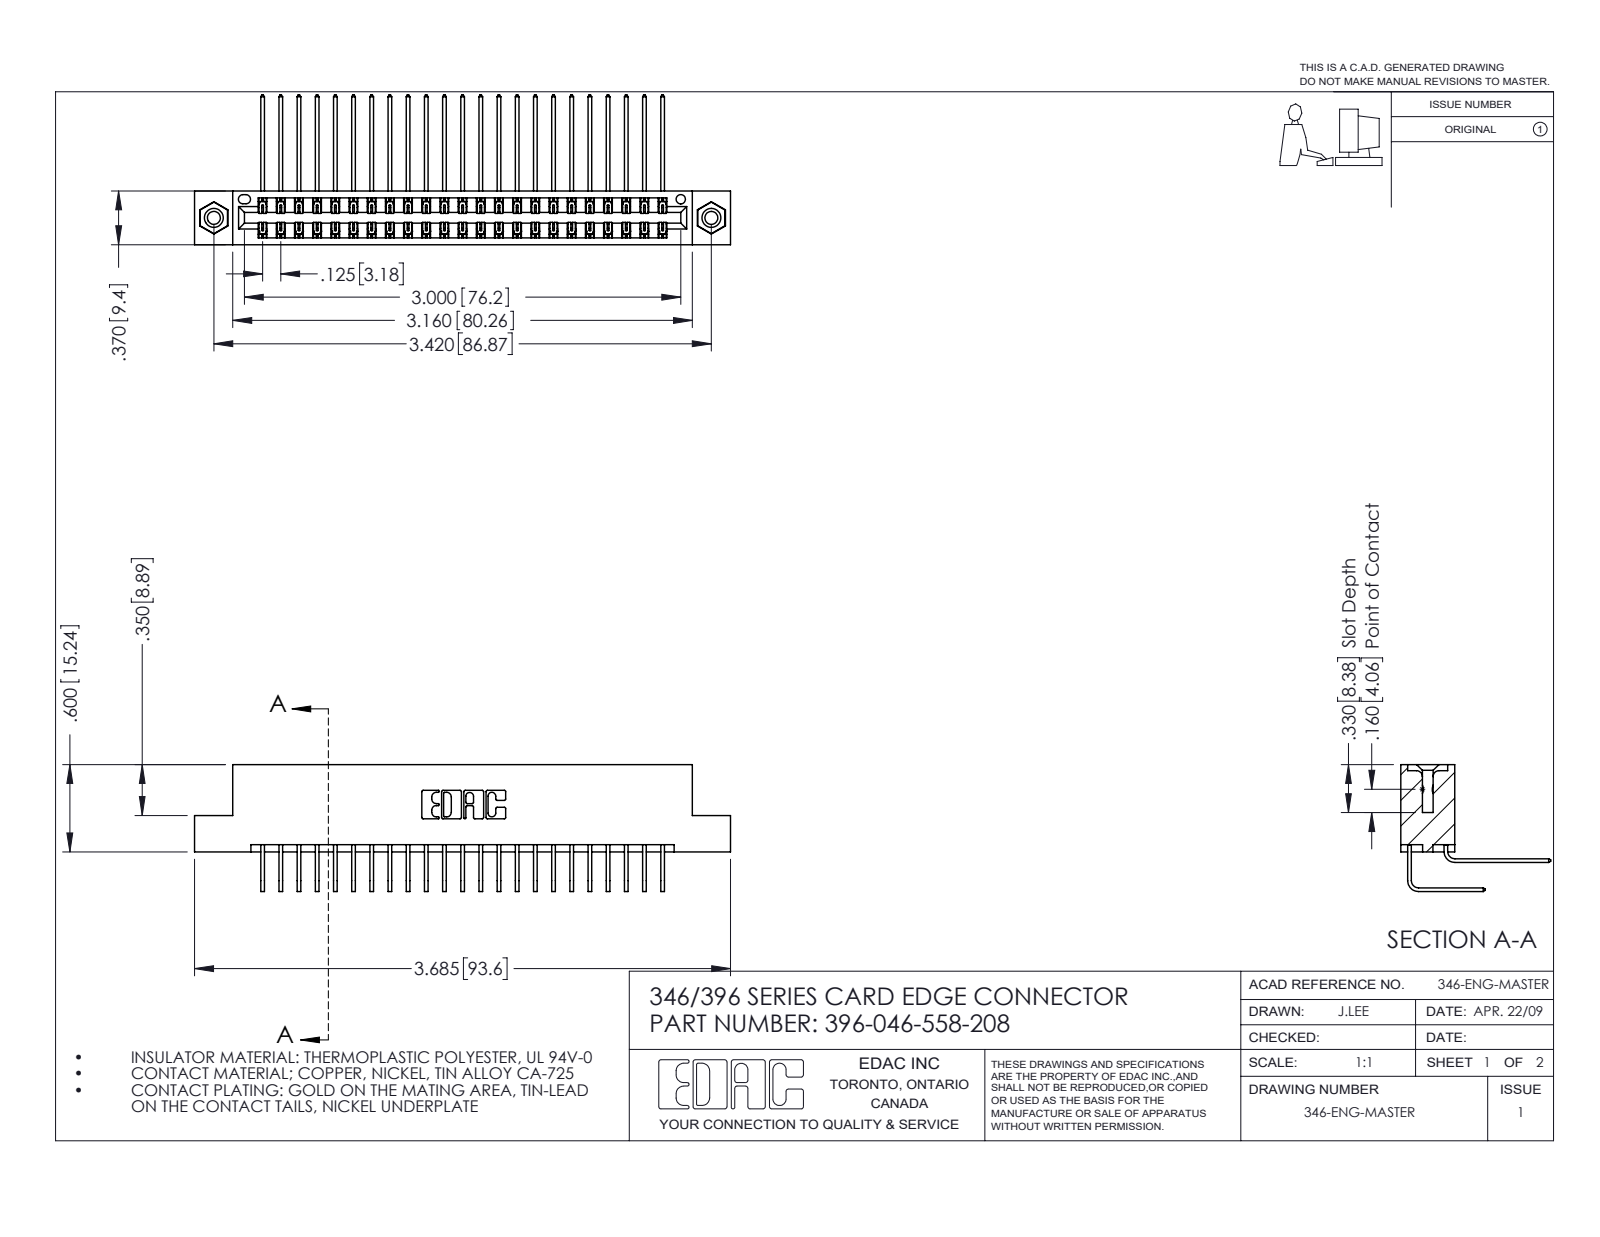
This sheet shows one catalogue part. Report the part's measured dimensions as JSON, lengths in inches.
{"part_name": "345-250-001_345-250-003-102; 345-292-001_558 559 Tail - 1; 396-046-558-208; 346 Part_Flush Mounting Lugs - 0.156 Dia-TI (+1 more)", "step_written_by": "SolidWorks 2016 (CONFIG_CONTROL_DESIGN)", "units": "inches", "bodies": {"solids": 49, "faces": 2666, "planar": 1810, "cylindrical": 840, "other": 16}, "overall_size": [3.685, 1.03, 0.873], "volume_in3": 0.564, "surface_area_in2": 21.22, "round_holes": [[0.089, 2], [0.125, 2], [0.156, 2], [0.064, 1]], "round_bosses_or_shafts": [[0.155, 2]], "partial_cylinders_radius": [[0.006, 69], [0.01, 22], [0.007, 6], [0.031, 6], [0.026, 3], [0.014, 2], [0.022, 2], [0.024, 2]], "face_to_face_distances": [0.322, 0.048, 0.25, 0.025, 0.37, 0.298, 0.072, 0.275, 0.148, 0.222], "hole_center_spacings": [0.246, 3.212, 3.42]}
